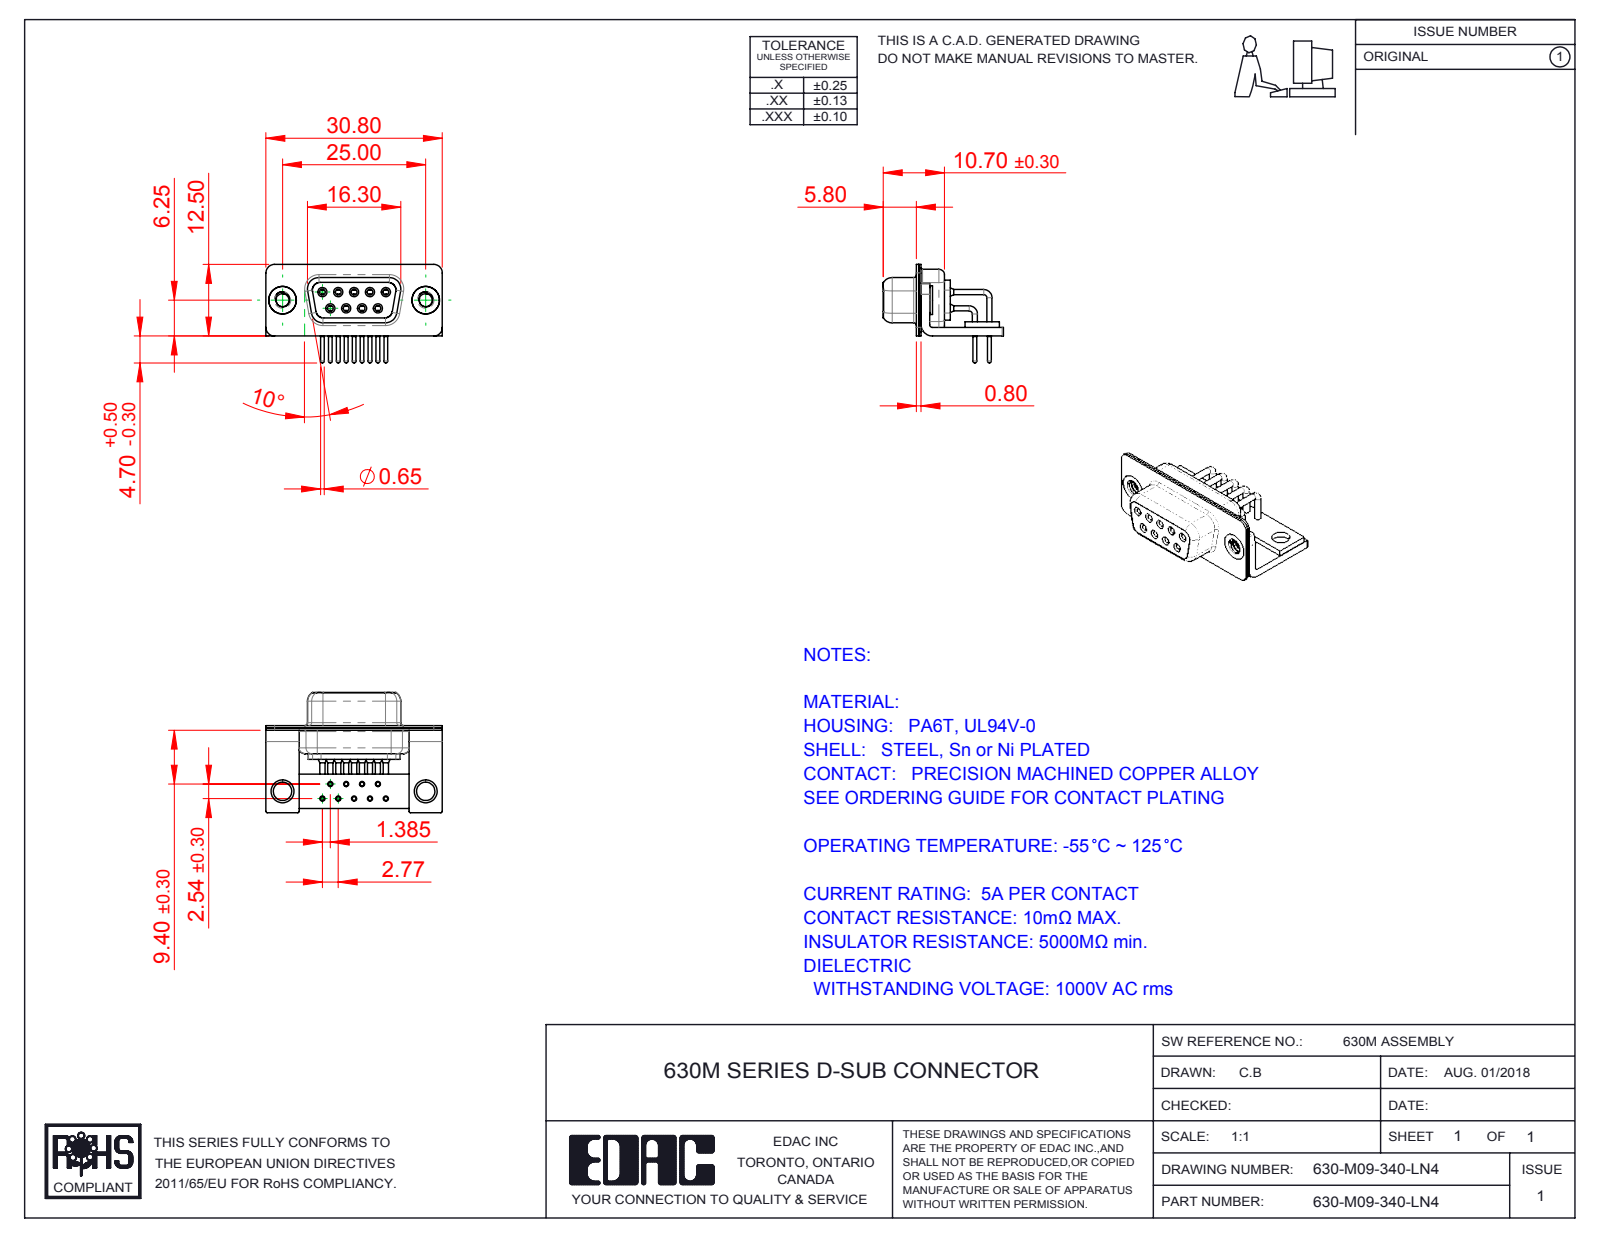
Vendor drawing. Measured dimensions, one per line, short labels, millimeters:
name: 630M Stabilizer Bracket; 630M Shell Rear_09 Contacts; 630M 4-40 Threaded Rivet_Stabilizer; 630M Contact Row 2 (+5 more)
written by: SolidWorks 2016 (CONFIG_CONTROL_DESIGN)
unit: mm
bodies: 17 solids, 824 faces (228 planar, 384 cylindrical, 212 other)
size: 30.8 × 21 × 17.2
volume: 2 191 mm³; area: 5 674 mm²
holes: 9× ⌀0.9, 9× ⌀1, 9× ⌀1.1, 9× ⌀1.7, 9× ⌀1.8, 9× ⌀2, 2× ⌀2.26, 2× ⌀3.2, 2× ⌀4, 2× ⌀4.8
bosses: 9× ⌀1.6, 9× ⌀1.5, 9× ⌀0.9, 9× ⌀0.65, 2× ⌀5, 2× ⌀4.9
rounds: 16× R0.25, 16× R1.5, 13× R2, 8× R1.35, 8× R1.6, 5× R0.5, 4× R0.6, 4× R0.65
face distances: 0.4, 0.8, 1.5, 2.3, 1.9, 1, 9.35, 1.45, 2.5, 8.95
hole spacings: 2.77, 5.54, 3.16, 4.87, 8.31, 2.89, 2.9, 5.03
